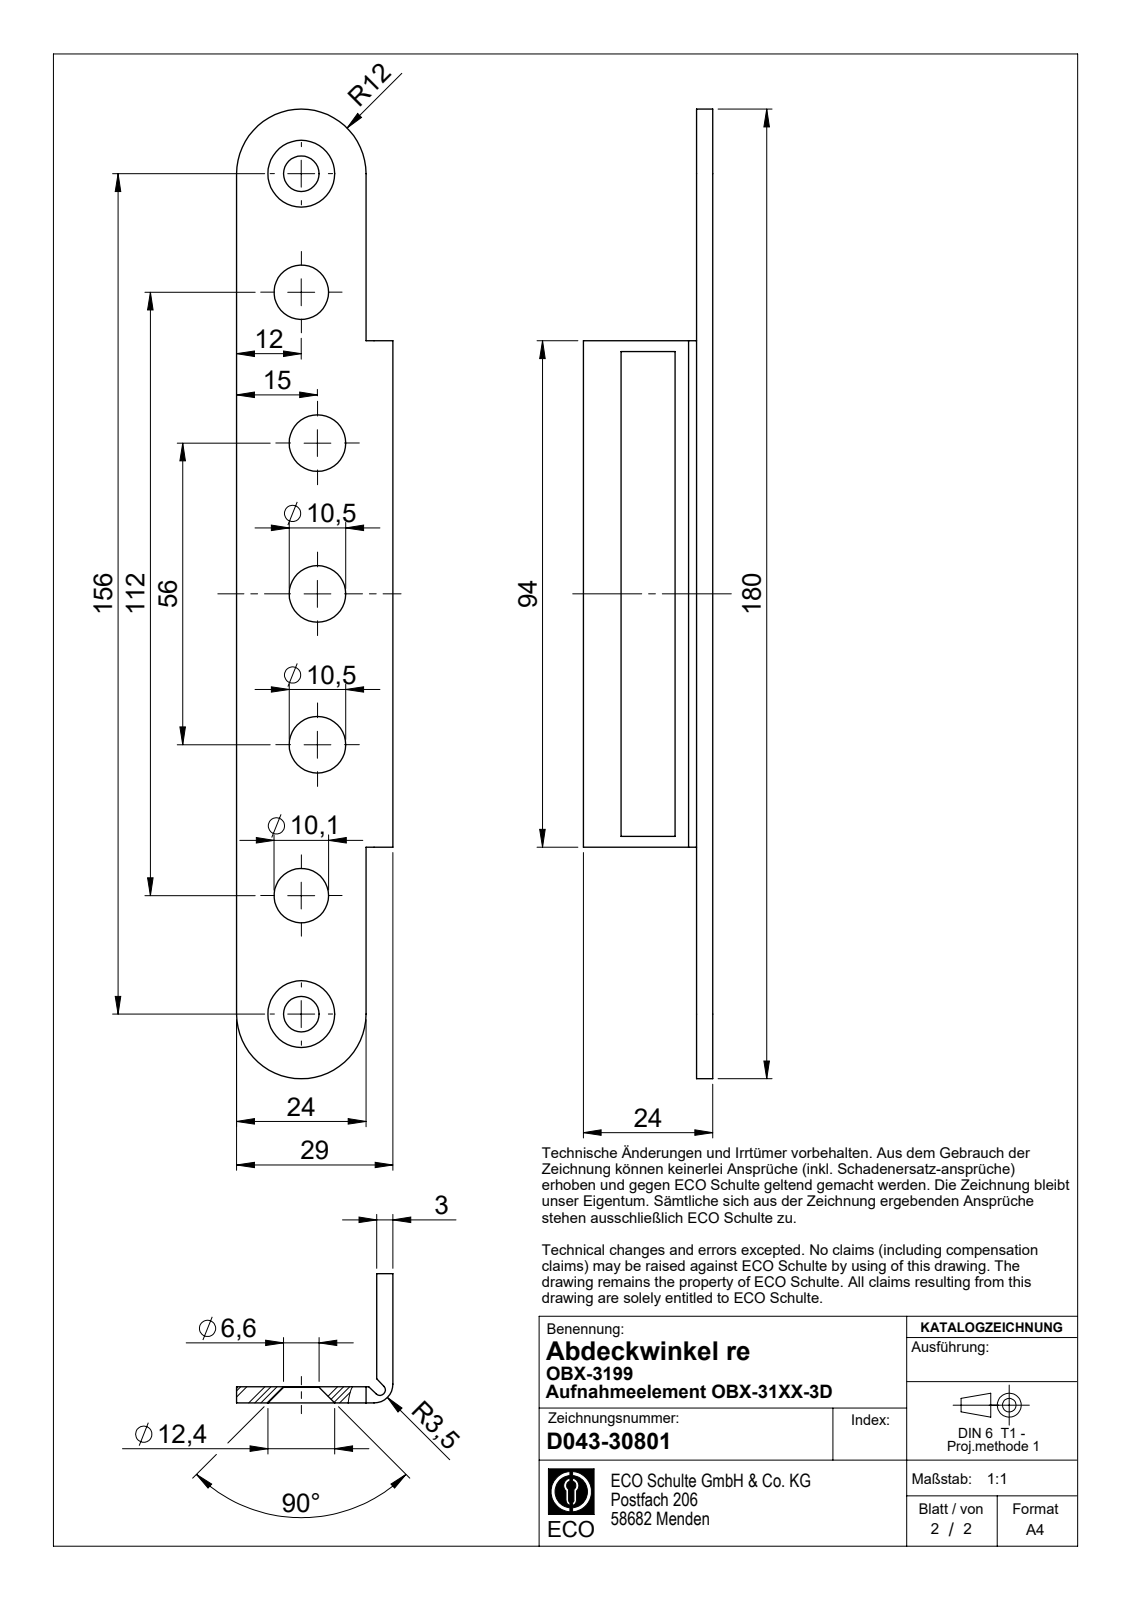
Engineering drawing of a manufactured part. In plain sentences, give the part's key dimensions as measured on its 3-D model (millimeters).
The part is named "OBX-3199-re_D043-30801". Its 3-D file was written by "SolidWorks 2020 (AUTOMOTIVE_DESIGN)". It is 1 solid with 35 faces: 14 planar, 17 cylindrical and 4 other. Overall it measures 180 by 29 by 24 millimeters. Its volume is 15 283 cubic millimeters and its surface area 12 839 square millimeters. Round holes: 3 of diameter 10.5, 2 of diameter 6.6, 2 of diameter 10.1. Partial cylindrical surfaces (rounded edges, fillets, slot ends): 2 of radius 12, 1 of radius 3.5. The main face-to-face distances are 3, 7, 17, 26, 29, 24, 21, 4, 10, 14. The hole center spacings are 22, 28, 28.16, 50.09, 56.08, 78.06, 84.05, 106.04.
